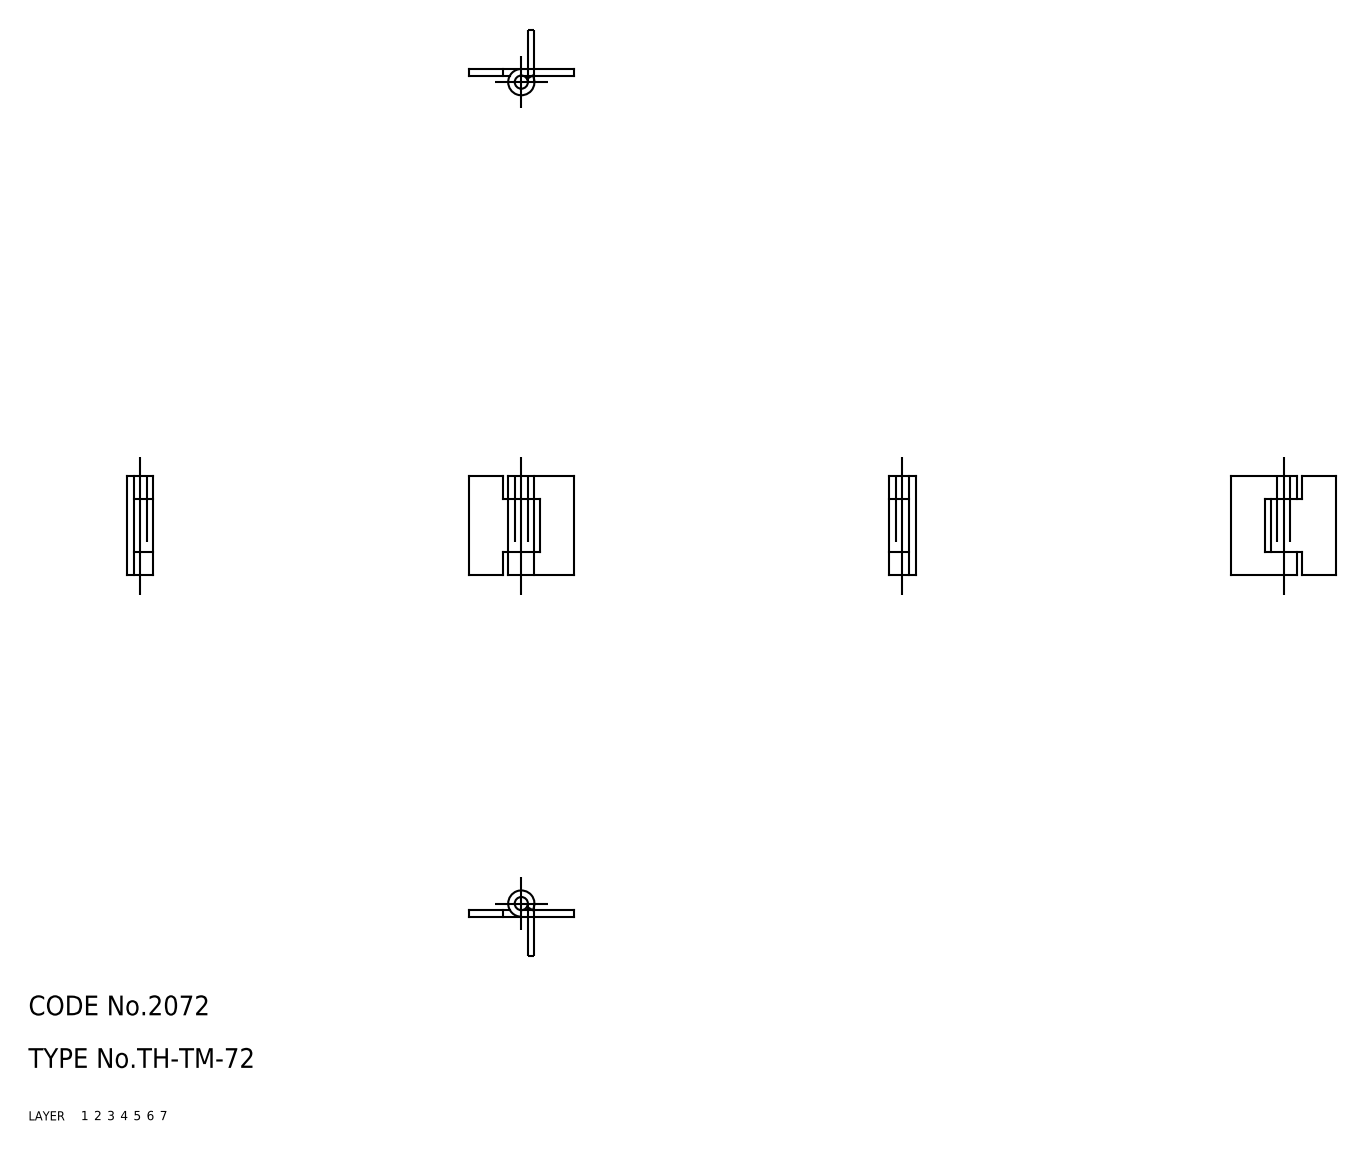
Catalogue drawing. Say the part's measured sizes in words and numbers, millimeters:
The part is named "hinge piece_B; hinge piece_A; shaft; TH_TM_72_25259_36". Its 3-D file was written by "CADfix (AUTOMOTIVE_DESIGN)". It is 3 solids with 30 faces: 0 planar, 0 cylindrical and 30 other. Overall it measures 16 by 15 by 4 millimeters. Its volume is 362 cubic millimeters and its surface area 875 square millimeters.
